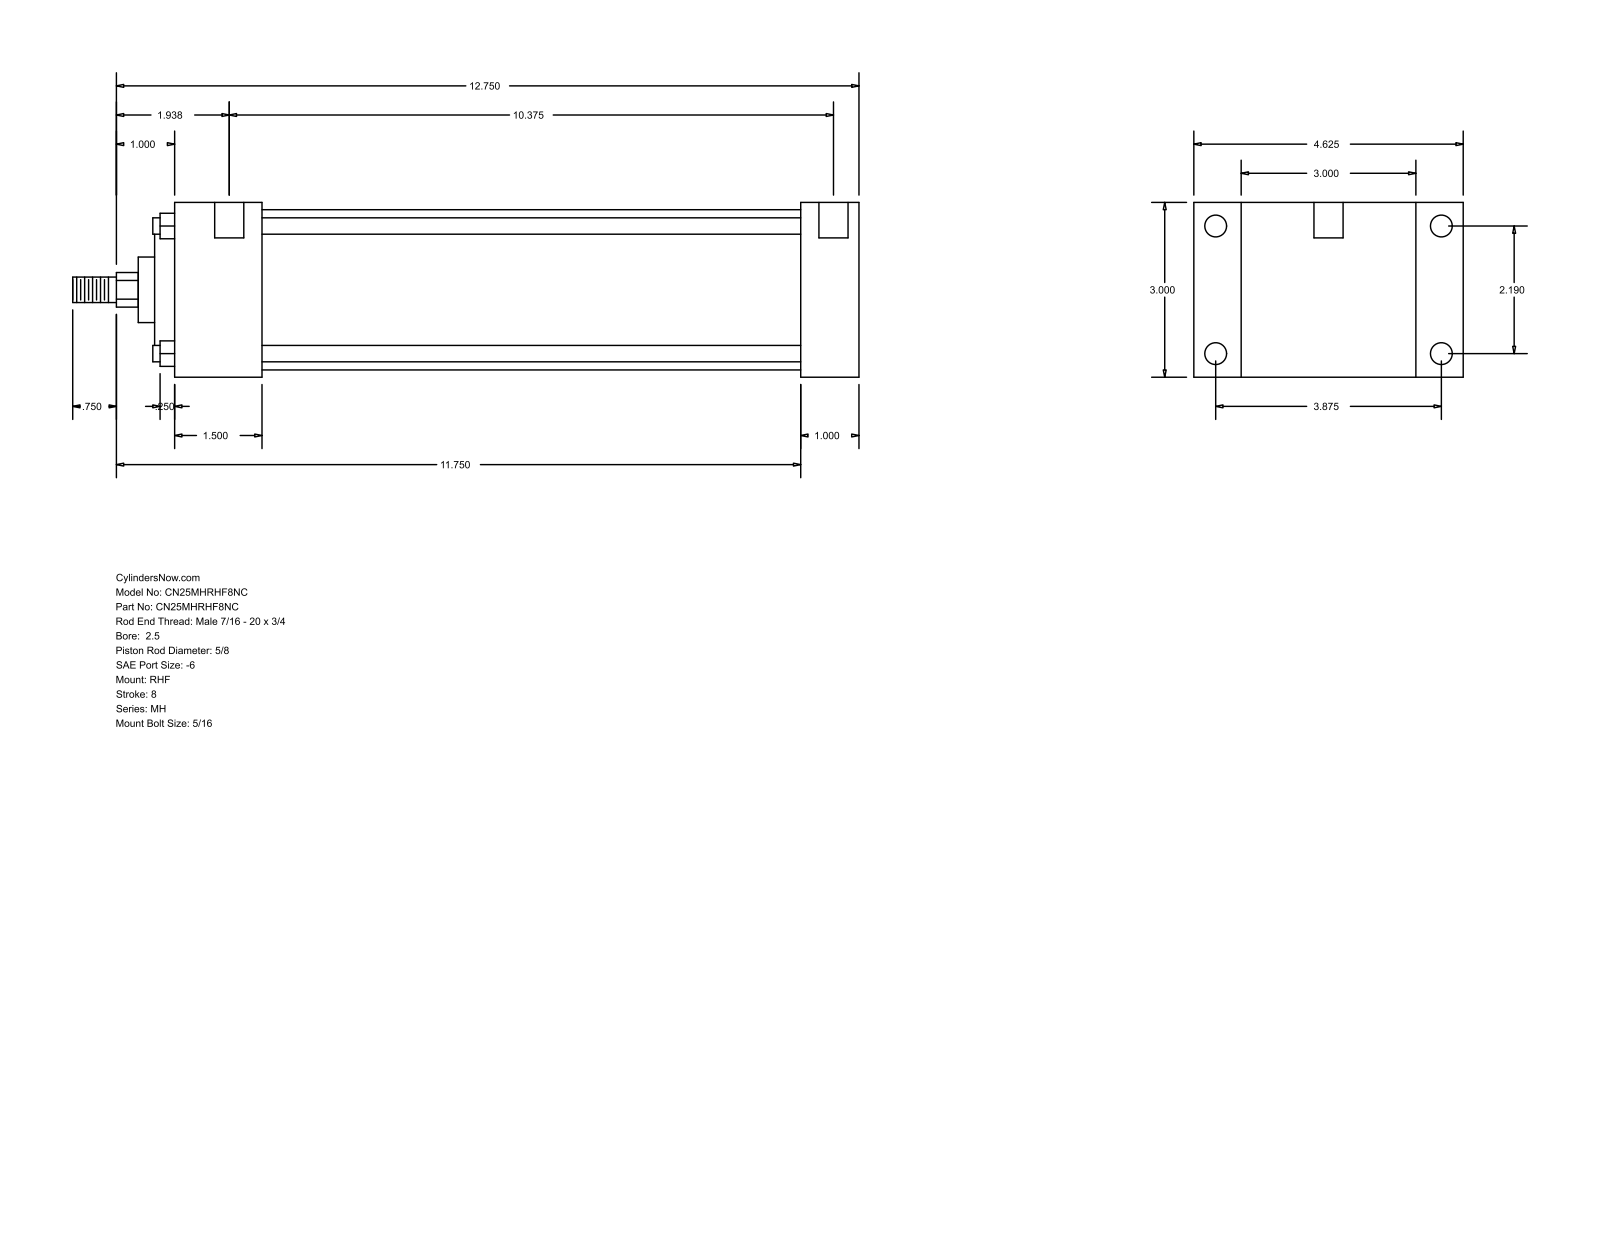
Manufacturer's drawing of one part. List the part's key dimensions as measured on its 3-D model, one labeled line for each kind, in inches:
Part name (STEP PRODUCT): MH_RHF__0250_0.625
STEP written by: GSSL Pune (CONFIG_CONTROL_DESIGN)
Units: inches
Bodies: 0 solids, 90 faces (61 planar, 29 cylindrical, 0 other)
Overall size (bounding box): 13.5 × 4.625 × 3
Round holes (diameter × count): ⌀0.219 ×4, ⌀0.375 ×4, ⌀0.5 ×2
Round bosses / shafts (diameter × count): ⌀0.281 ×4, ⌀2.75 ×1, ⌀2.187 ×1, ⌀1.125 ×1, ⌀0.625 ×1, ⌀0.437 ×1
Partial cylindrical surfaces — rounded edges, fillets, slot ends (radius × count): R0.297 ×1
Main face-to-face distances: 3, 1, 0.813, 3.813, 11.75, 10.75, 1.5, 4.625, 9.25, 10.25
Hole centre spacings: 2.19, 3.875, 4.451, 10.687, 0.125, 0.187, 10.375, 10.5
